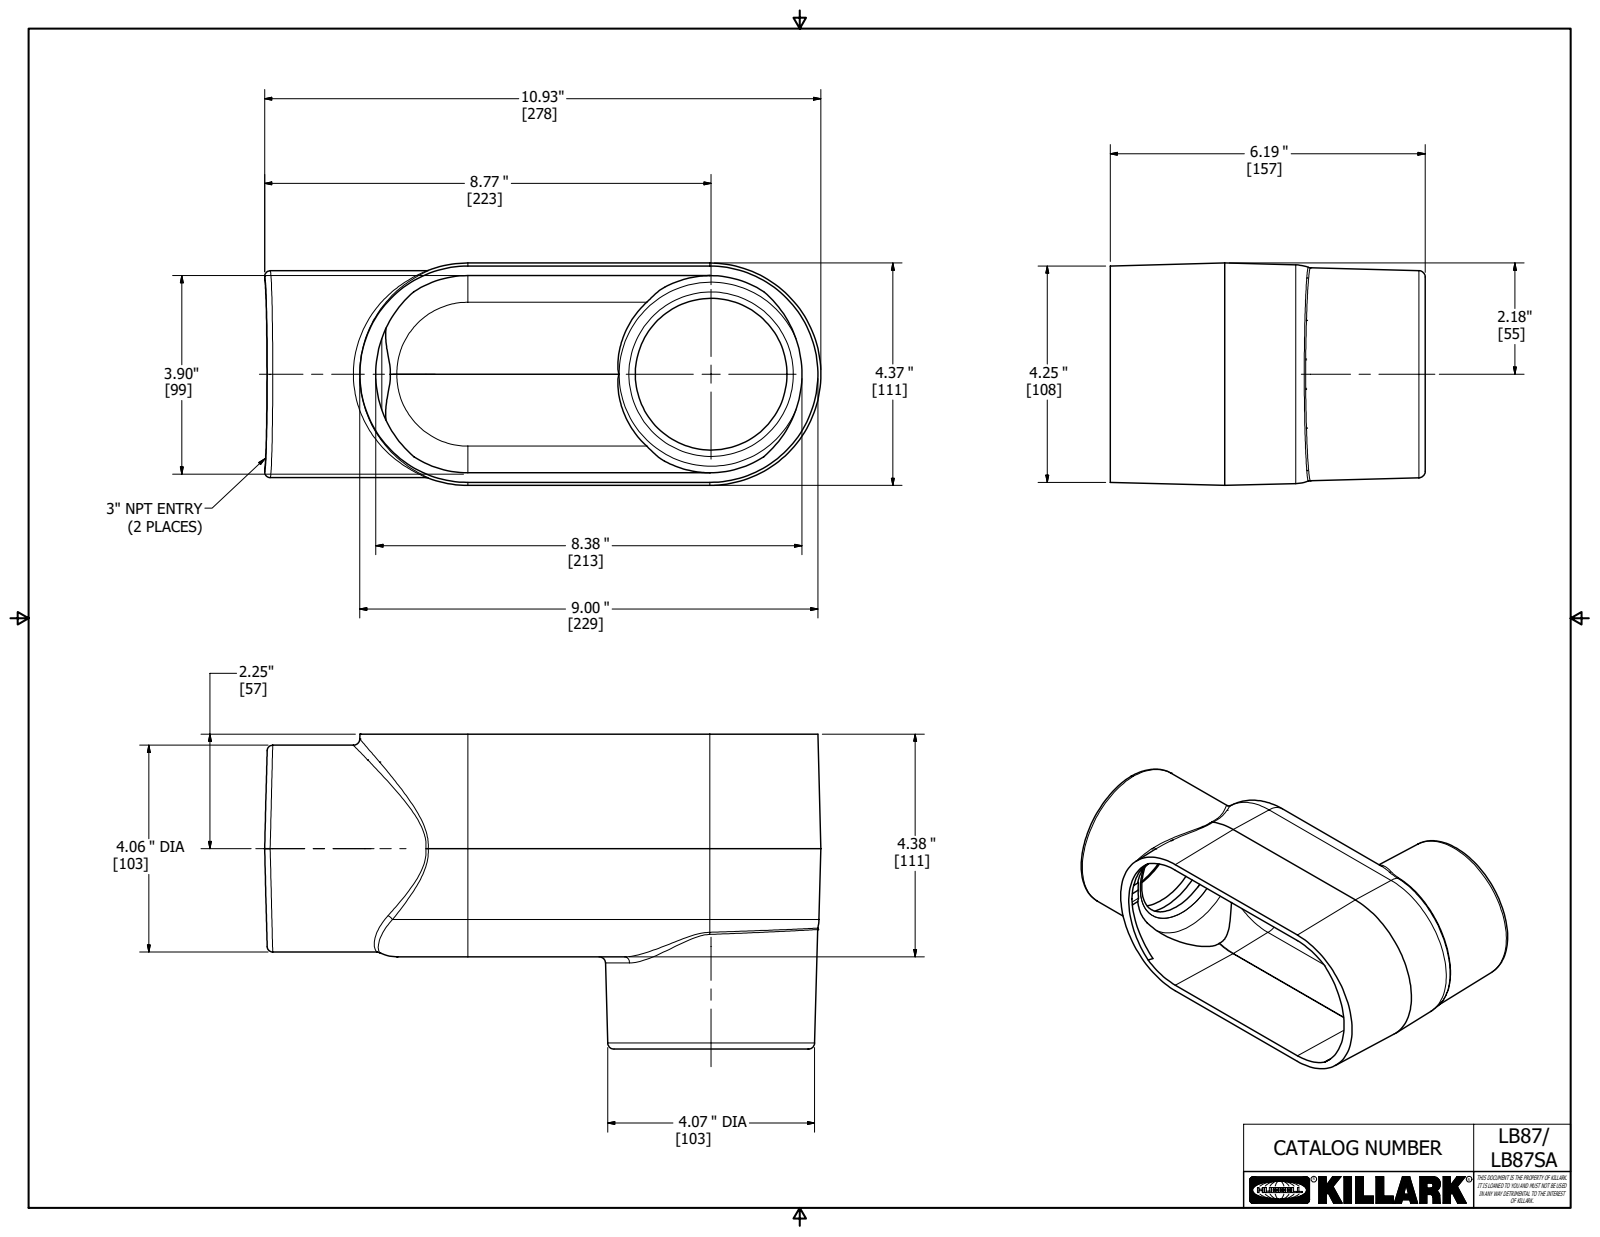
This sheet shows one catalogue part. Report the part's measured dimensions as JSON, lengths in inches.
{"part_name": "17723", "step_written_by": "Autodesk Inventor 2018 (AUTOMOTIVE_DESIGN)", "units": "inches", "bodies": {"solids": 1, "faces": 101, "planar": 32, "cylindrical": 23, "other": 46}, "overall_size": [10.93, 6.188, 4.368], "volume_in3": 36.99, "surface_area_in2": 320, "round_holes": [[3.511, 2], [3.844, 1]], "round_bosses_or_shafts": [[4.062, 1]], "partial_cylinders_radius": [[0.05, 6], [0.125, 4], [0.5, 2], [0.562, 2], [0.75, 2], [2.125, 2], [1.937, 1]], "face_to_face_distances": [0.187, 4.18, 4.368, 3.993, 4.375, 4.187, 0.031, 0.157, 4.344, 2]}
